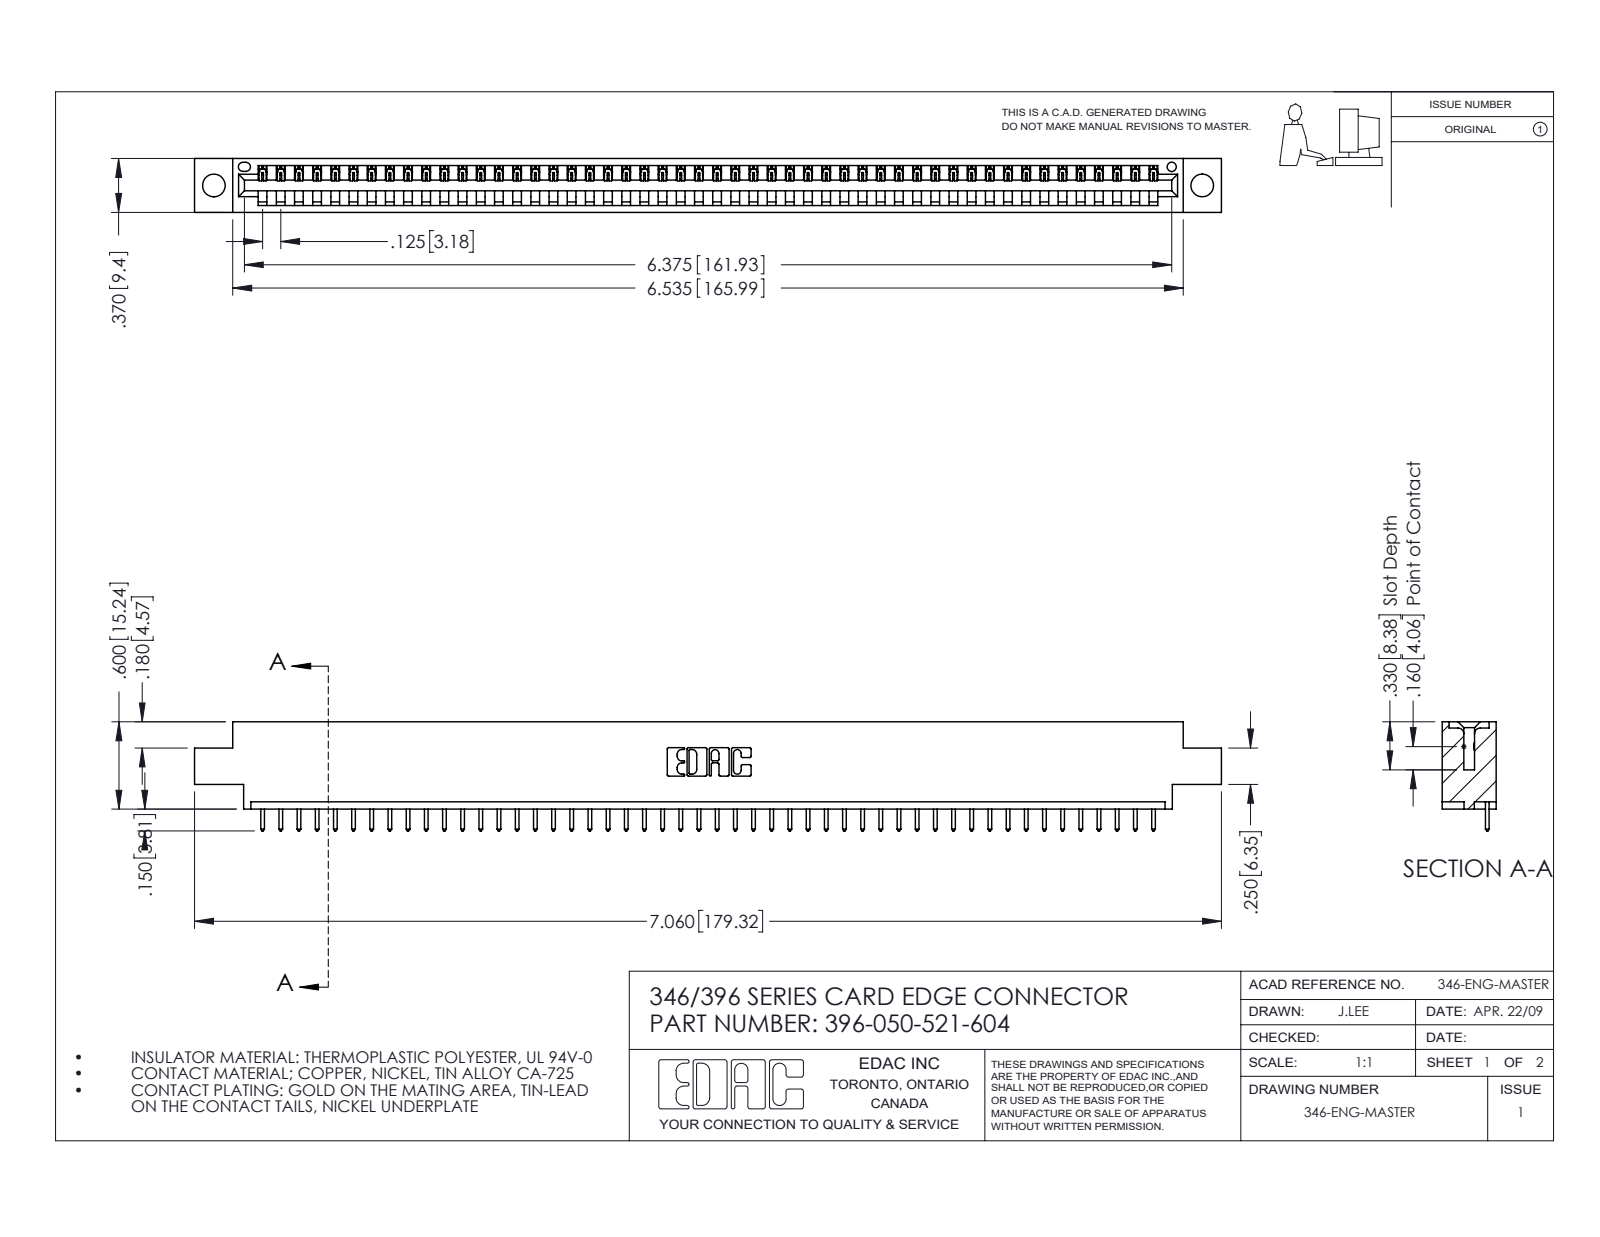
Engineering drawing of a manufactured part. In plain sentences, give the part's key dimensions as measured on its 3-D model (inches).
The part is named "396-050-521-604; 345-292-001_345-293-121; 346 Part_0.170 Offset - 0.156 Dia-TH". Its 3-D file was written by "SolidWorks 2016 (CONFIG_CONTROL_DESIGN)". It is 51 solids with 3026 faces: 2080 planar, 946 cylindrical and 0 other. Overall it measures 7.06 by 0.75 by 0.37 inches. Its volume is 1.027 cubic inches and its surface area 31.82 square inches. Round holes: 2 of diameter 0.156, 1 of diameter 0.064. Partial cylindrical surfaces (rounded edges, fillets, slot ends): 100 of radius 0.006, 100 of radius 0.01, 22 of radius 0.01, 6 of radius 0.007, 6 of radius 0.031, 3 of radius 0.026, 2 of radius 0.031, 2 of radius 0.04. The main face-to-face distances are 0.048, 0.322, 0.37, 0.25, 0.072, 0.298, 0.025, 0.148, 0.222, 0.1. The hole center spacings are 0.246, 6.586, 6.795.
